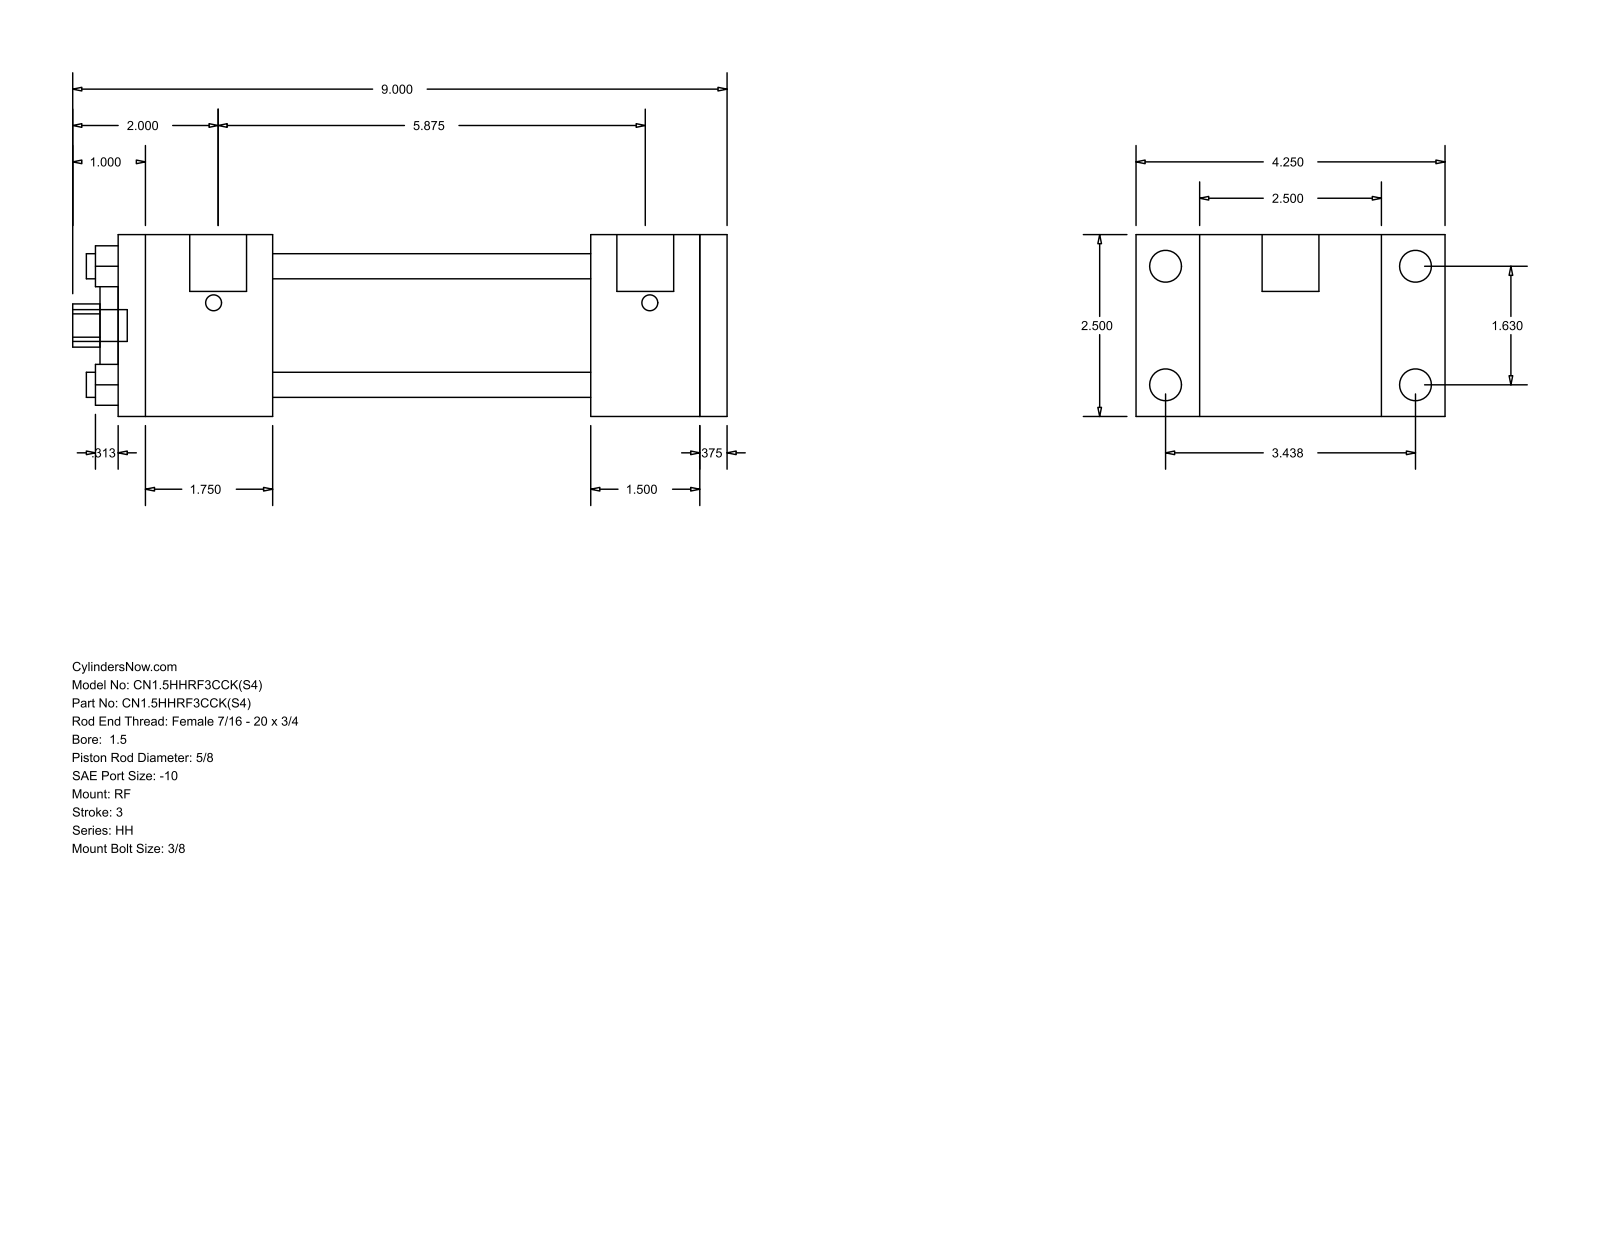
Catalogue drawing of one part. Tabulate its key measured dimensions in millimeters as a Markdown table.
| quantity | value |
| --- | --- |
| part name | HH_RF__0150_0.625 |
| STEP written by | GSSL Pune (CONFIG_CONTROL_DESIGN) |
| units | millimeters |
| bodies | 0 solids, 92 faces (64 planar, 28 cylindrical, 0 other) |
| overall size | 228.6 × 107.95 × 63.5 |
| round holes (diameter × count) | 8.76 × 4, 15.88 × 1, 28.57 × 1, 44.45 × 1 |
| round bosses / shafts (diameter × count) | 11.13 × 4, 5.56 × 4, 19.84 × 2, 11.11 × 1 |
| partial cylindrical surfaces (radius × count) | 7.54 × 1 |
| main face-to-face distances | 63.5, 212.72, 9.53, 38.1, 203.19, 47.63, 53.97, 165.09, 111.12, 149.22 |
| hole center spacings | 29.27, 41.4, 58.55 |
